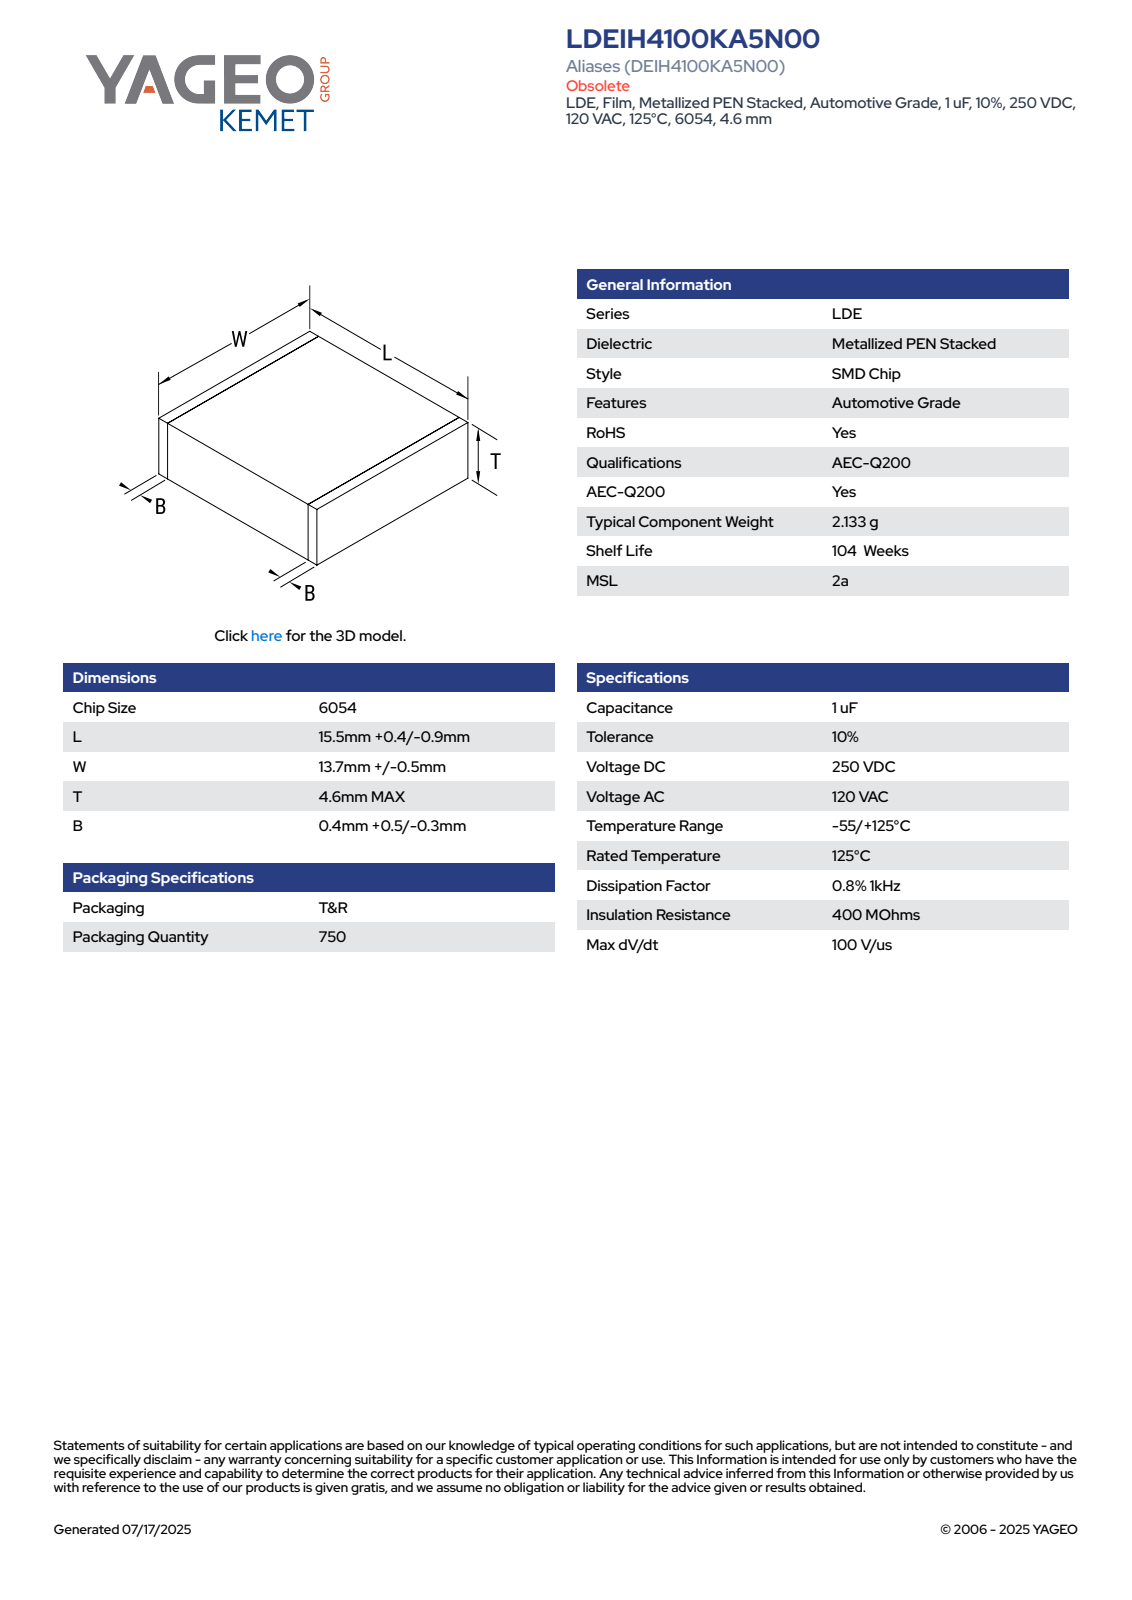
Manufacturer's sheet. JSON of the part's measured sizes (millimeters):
{"part_name": "CFS_LDELDB_6054_L15.9W14.2T4.6B0.9", "step_written_by": "SolidWorks 2020 (AUTOMOTIVE_DESIGN)", "units": "millimeters", "bodies": {"solids": 4, "faces": 73, "planar": 73, "cylindrical": 0, "other": 0}, "overall_size": [15.9, 14.2, 4.6], "volume_mm3": 1033, "surface_area_mm2": 740, "face_to_face_distances": [4.58, 14.18, 15.9, 4.59, 4.6, 14.19, 14.2, 0.5, 15.4, 14.9]}
